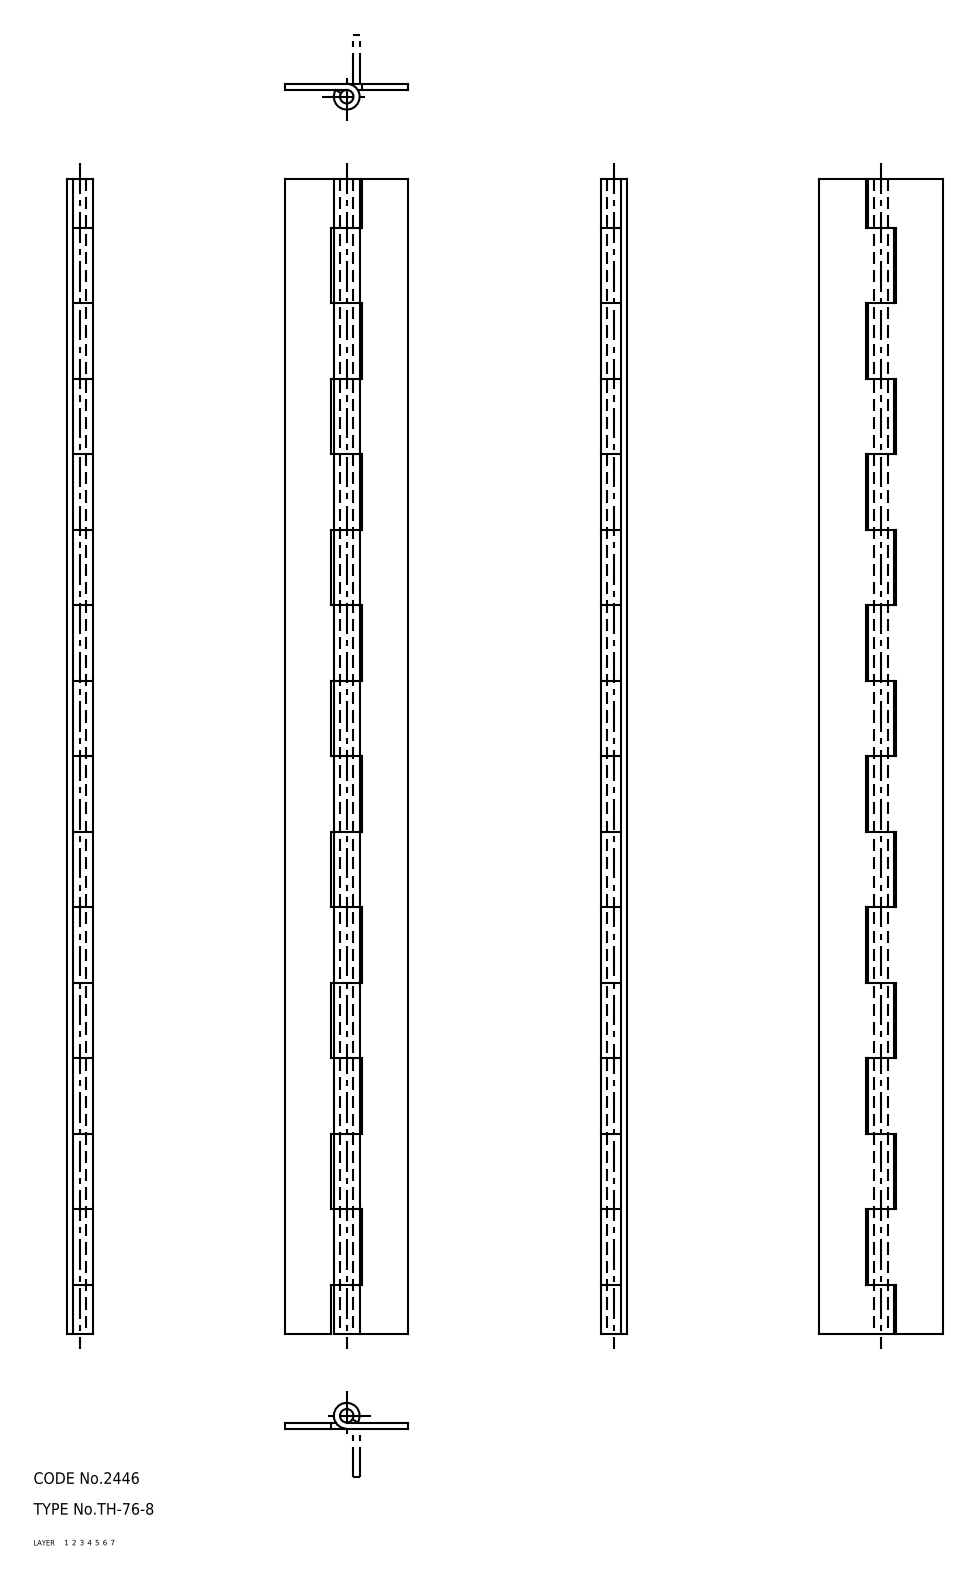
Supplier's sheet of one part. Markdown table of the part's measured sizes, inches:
| quantity | value |
| --- | --- |
| part name | hinge piece_B; hinge piece_A; shaft; TH_76_8 |
| STEP written by | SolidWorks 2015 (AUTOMOTIVE_DESIGN) |
| units | inches |
| bodies | 3 solids, 108 faces (74 planar, 34 cylindrical, 0 other) |
| overall size | 11.811 × 1.26 × 0.264 |
| volume | 1.387 in³ |
| surface area | 48.05 in² |
| round holes (diameter × count) | 0.138 × 1 |
| round bosses / shafts (diameter × count) | 0.264 × 1 |
| main face-to-face distances | 0.063, 0.772, 1.543, 2.315, 3.087, 3.858, 4.63, 1.26, 0.472, 0.787 |
